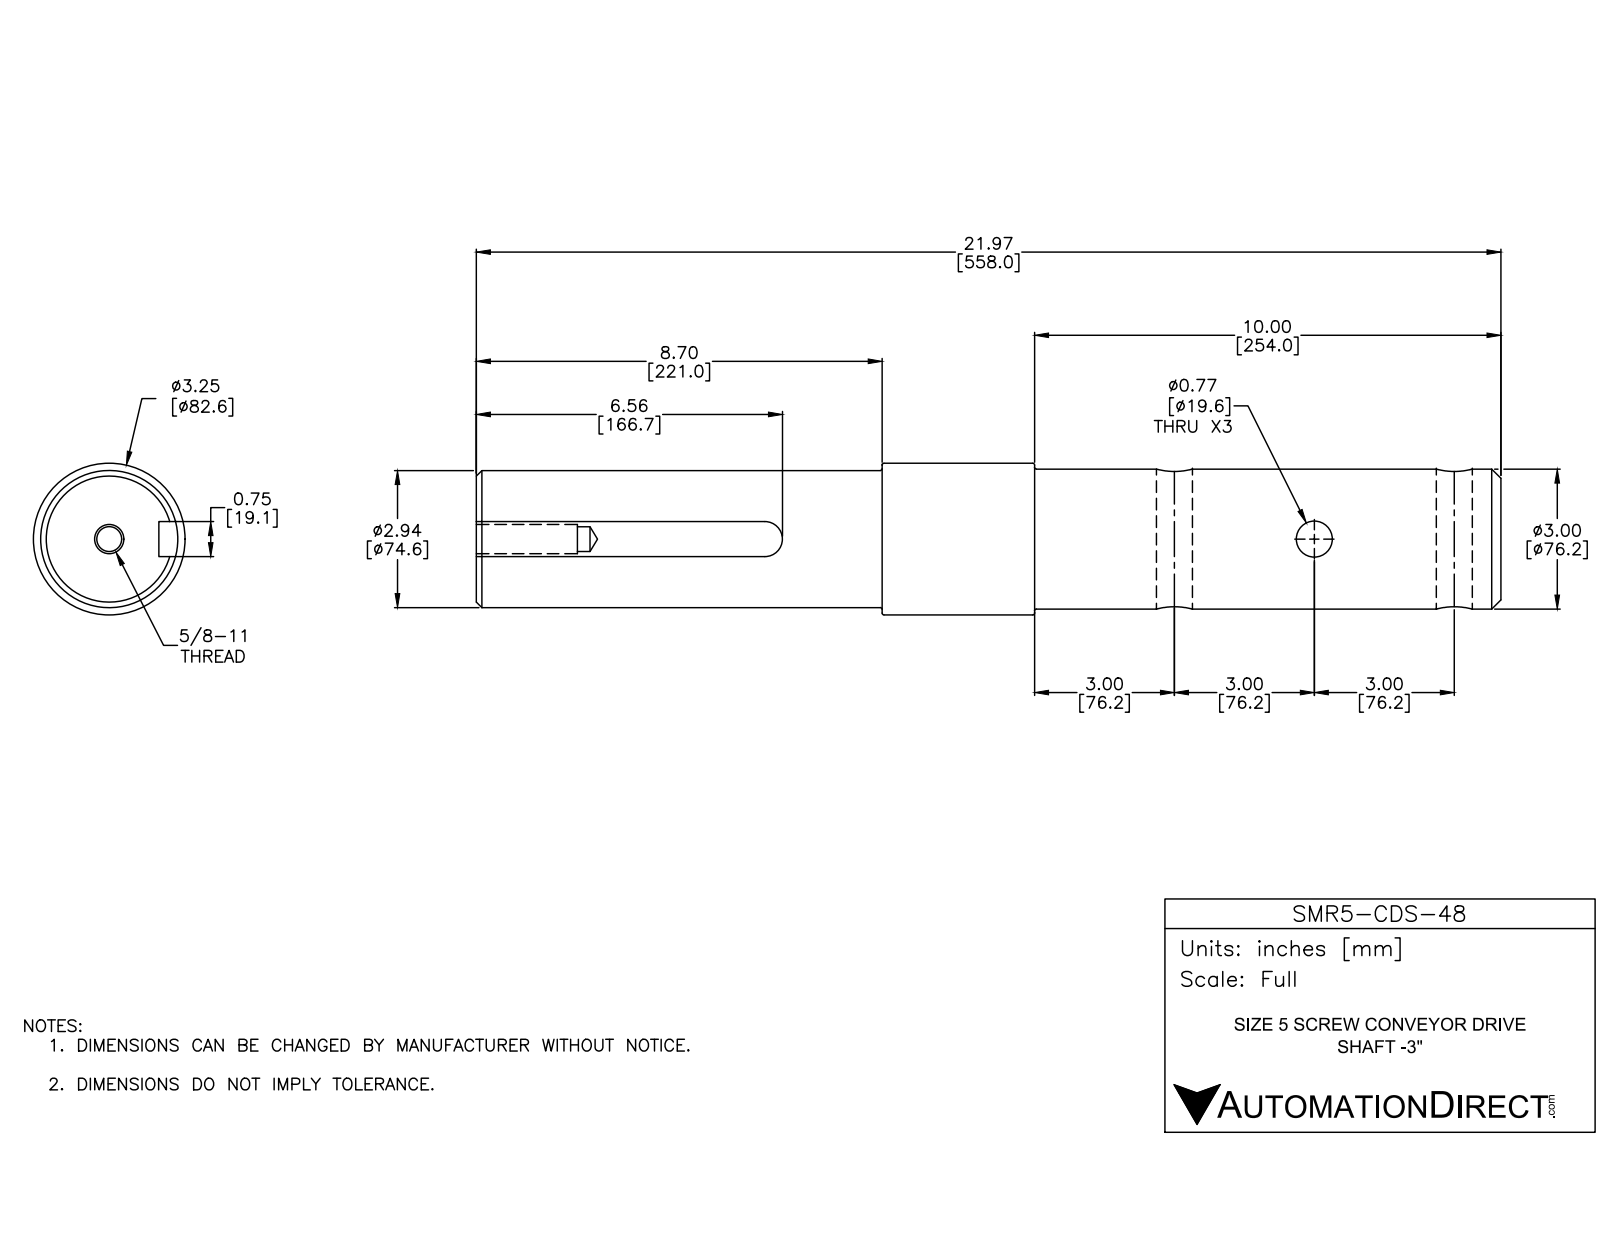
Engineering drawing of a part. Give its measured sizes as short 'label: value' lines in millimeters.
name: SMR5-CDS-48
written by: SolidWorks 2016 (AUTOMOTIVE_DESIGN)
unit: mm
bodies: 1 solid, 40 faces (8 planar, 18 cylindrical, 14 other)
size: 558 × 82.6 × 82.6
volume: 2 453 000 mm³; area: 161 300 mm²
holes: 3× ⌀19.6, 1× ⌀13.5, 1× ⌀15.9
bosses: 1× ⌀82.6, 1× ⌀76.2, 1× ⌀74.6
rounds: 1× R9.5
face distances: 558, 19.1, 221, 337, 304, 83, 253.9, 55, 166, 249
hole spacings: 152.4
